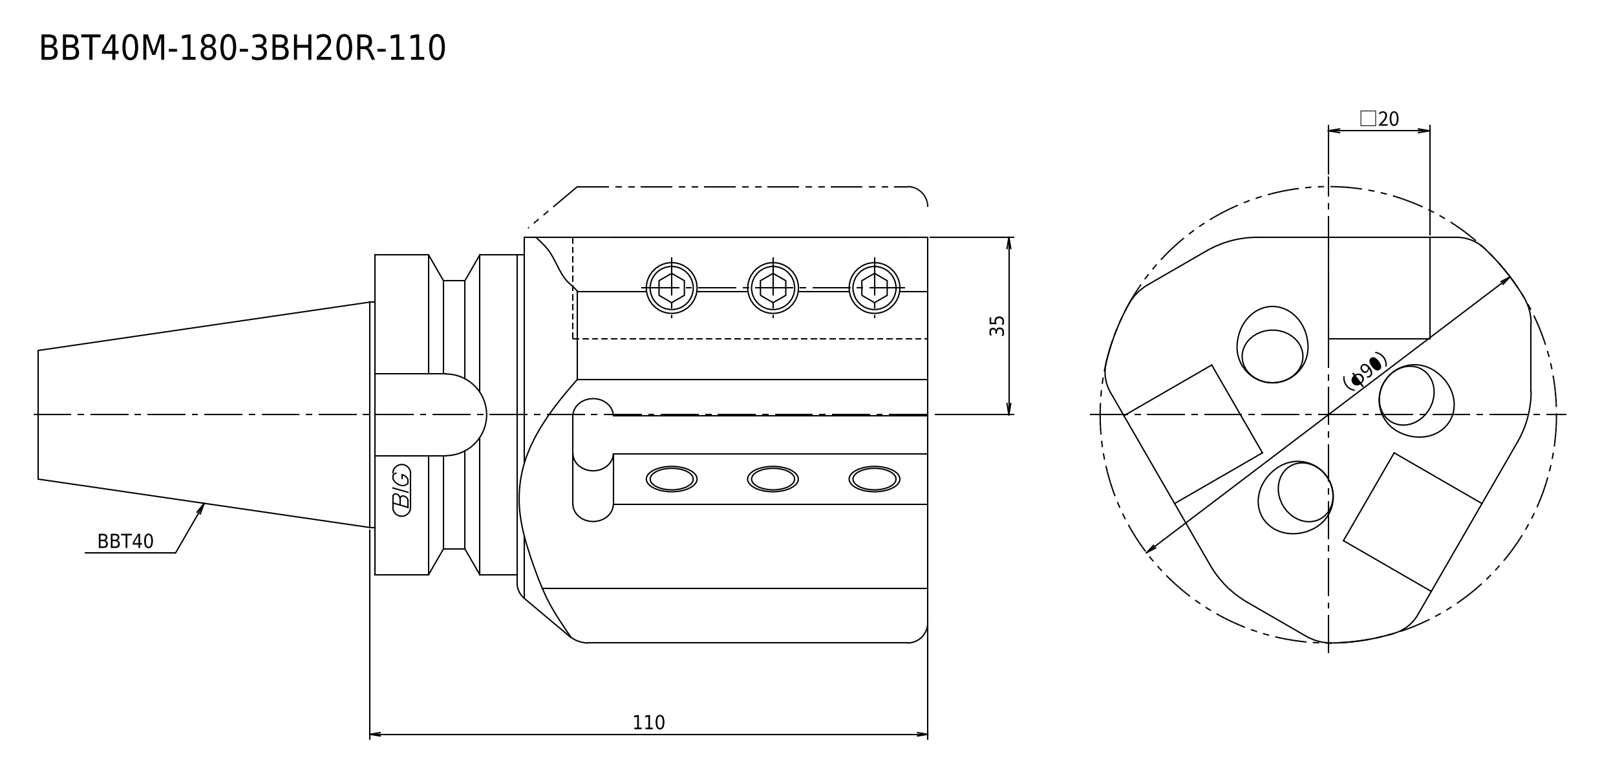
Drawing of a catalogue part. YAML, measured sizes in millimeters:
step_written_by: "Kubotek KeyCreator 2011 V10.0.2 (22737) (automotive_design)"
units: millimeters
bodies: {solids: 1, faces: 35, planar: 22, cylindrical: 7, other: 6}
overall_size: [175.4, 84.45, 80]
volume: 465290
surface_area: 51523
round_bosses_or_shafts:
  - {diameter: 63, count: 1}
  - {diameter: 53, count: 1}
  - {diameter: 44.45, count: 1}
partial_cylinders:
  - {radius: 45, count: 1}
face_to_face_distances: [20, 40, 109, 70, 39, 81, 11, 28, 175.4, 105.4]
